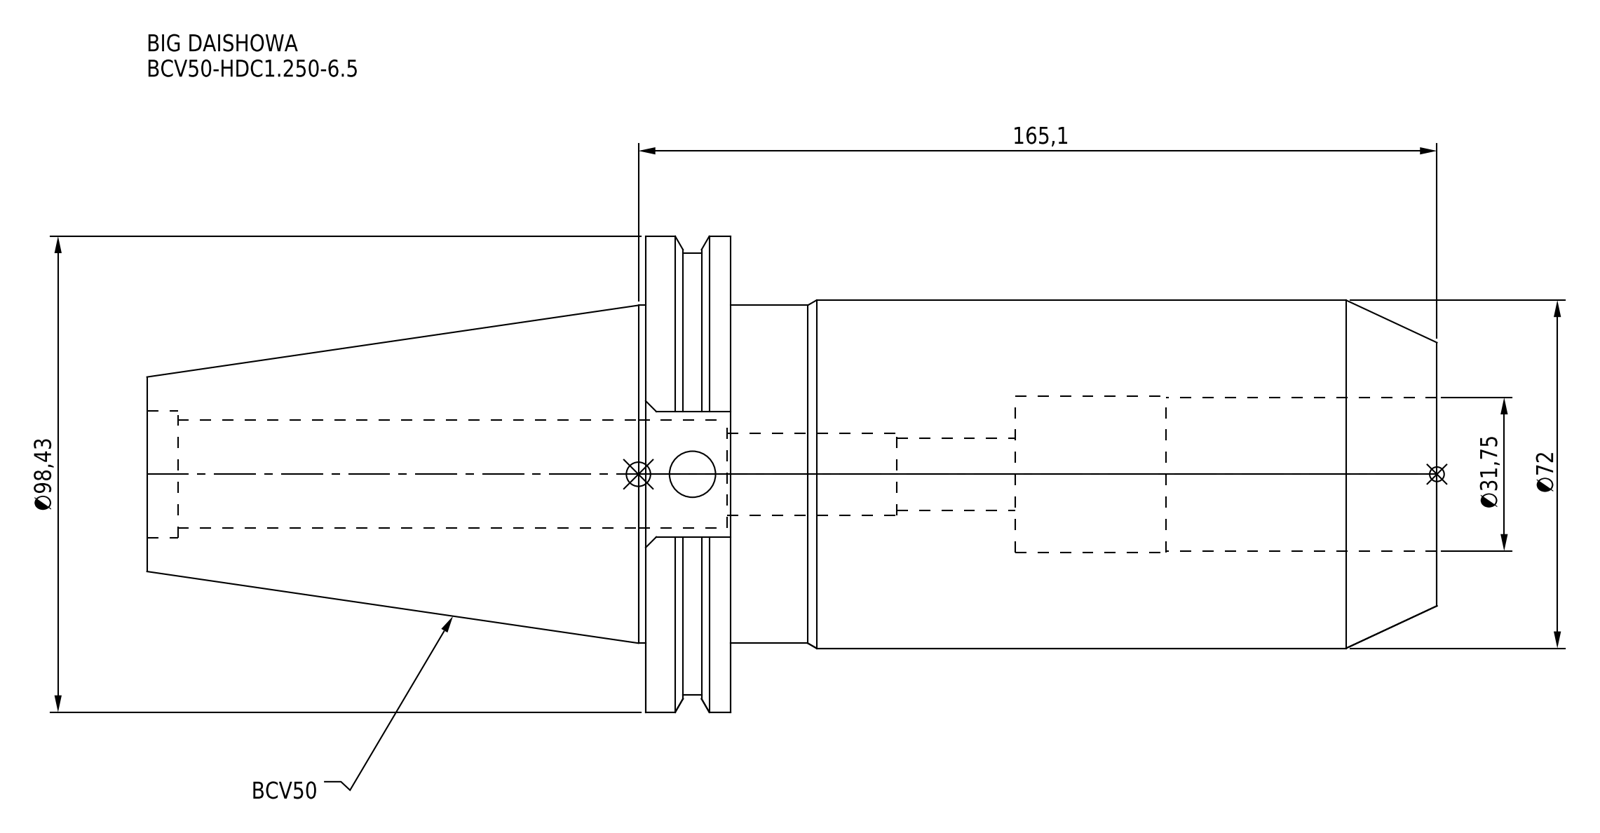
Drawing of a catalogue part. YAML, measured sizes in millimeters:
part_name: "BCV50-HDC1_250-6_5"
step_written_by: "CREO PARAMETRIC BY PTC INC, 2016380 (AUTOMOTIVE_DESIGN)"
units: millimeters
bodies: {solids: 1, faces: 62, planar: 24, cylindrical: 28, other: 10}
overall_size: [266.7, 98.42, 94.95]
volume: 814548
surface_area: 87907
round_holes:
  - {diameter: 9.53, count: 1}
  - {diameter: 15, count: 1}
  - {diameter: 17, count: 1}
  - {diameter: 22.3, count: 1}
  - {diameter: 26.23, count: 1}
  - {diameter: 31.75, count: 1}
  - {diameter: 32.3, count: 1}
round_bosses_or_shafts:
  - {diameter: 98.42, count: 1}
  - {diameter: 91.29, count: 1}
  - {diameter: 72, count: 1}
  - {diameter: 69.85, count: 1}
face_to_face_distances: [17.55, 146.05, 163.6, 266.7, 120.65, 103.1, 87.2, 58.85, 76.4, 179.5]
